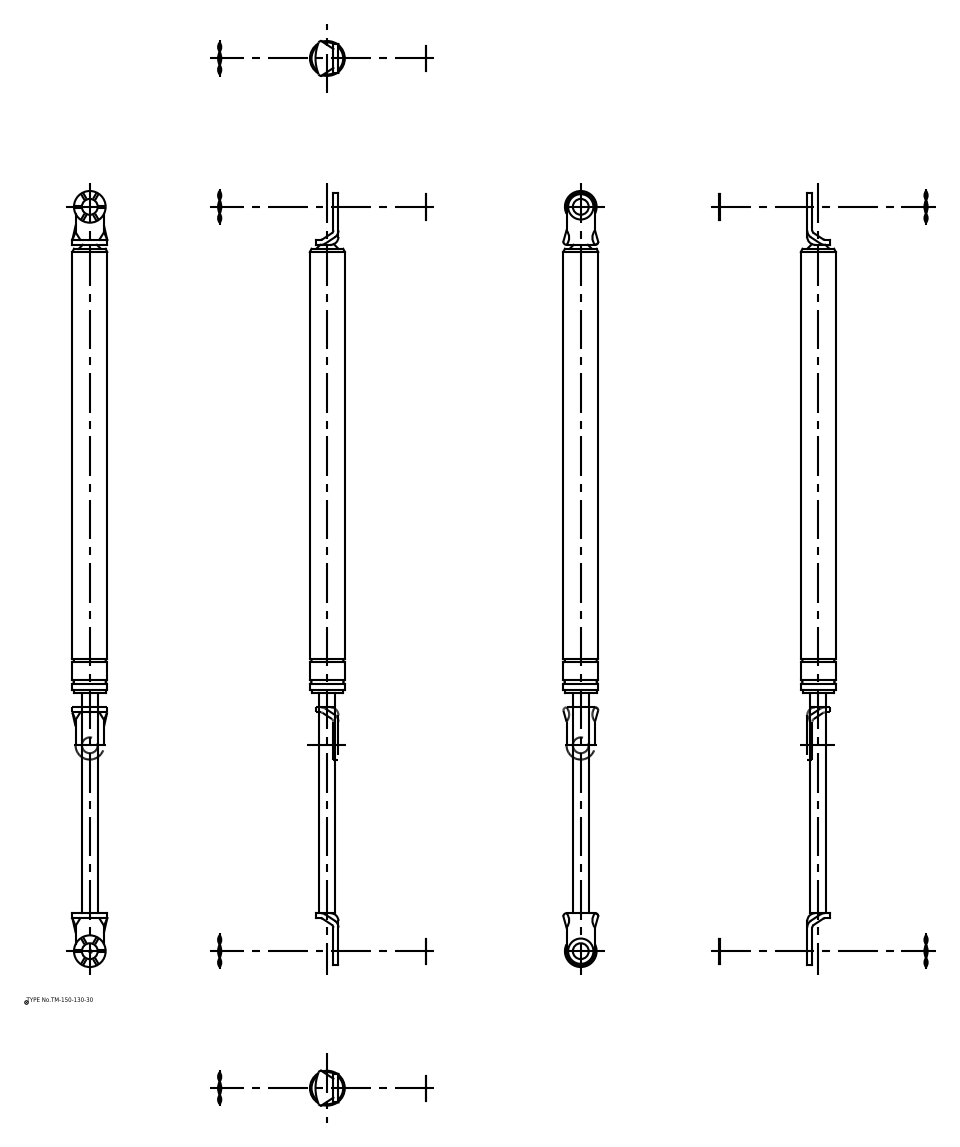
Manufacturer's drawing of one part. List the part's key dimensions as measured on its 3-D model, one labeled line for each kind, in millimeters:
Part name (STEP PRODUCT): ウェーブワッシャー; ワッシャー; 本体; 本体_div
STEP written by: spGate 16.7.1 (AUTOMOTIVE_DESIGN)
Units: millimetres
Bodies: 6 solids, 94 faces (42 planar, 44 cylindrical, 8 other)
Overall size (bounding box): 490 × 22.5 × 22.5
Volume: 123 331 mm³ · Surface area: 30 253 mm²
Round holes (diameter × count): ⌀10 ×2
Round bosses / shafts (diameter × count): ⌀20 ×3, ⌀16 ×2, ⌀22.5 ×1, ⌀22 ×1, ⌀10 ×1
Partial cylindrical surfaces — rounded edges, fillets, slot ends (radius × count): R4.4 ×2, R5 ×2, R9 ×2, R26.32 ×1
Main face-to-face distances: 3.2, 2, 5.2, 425.2, 5.7, 3.7, 0.5, 286.2, 142.2, 428.4
Hole centre spacings: 470
